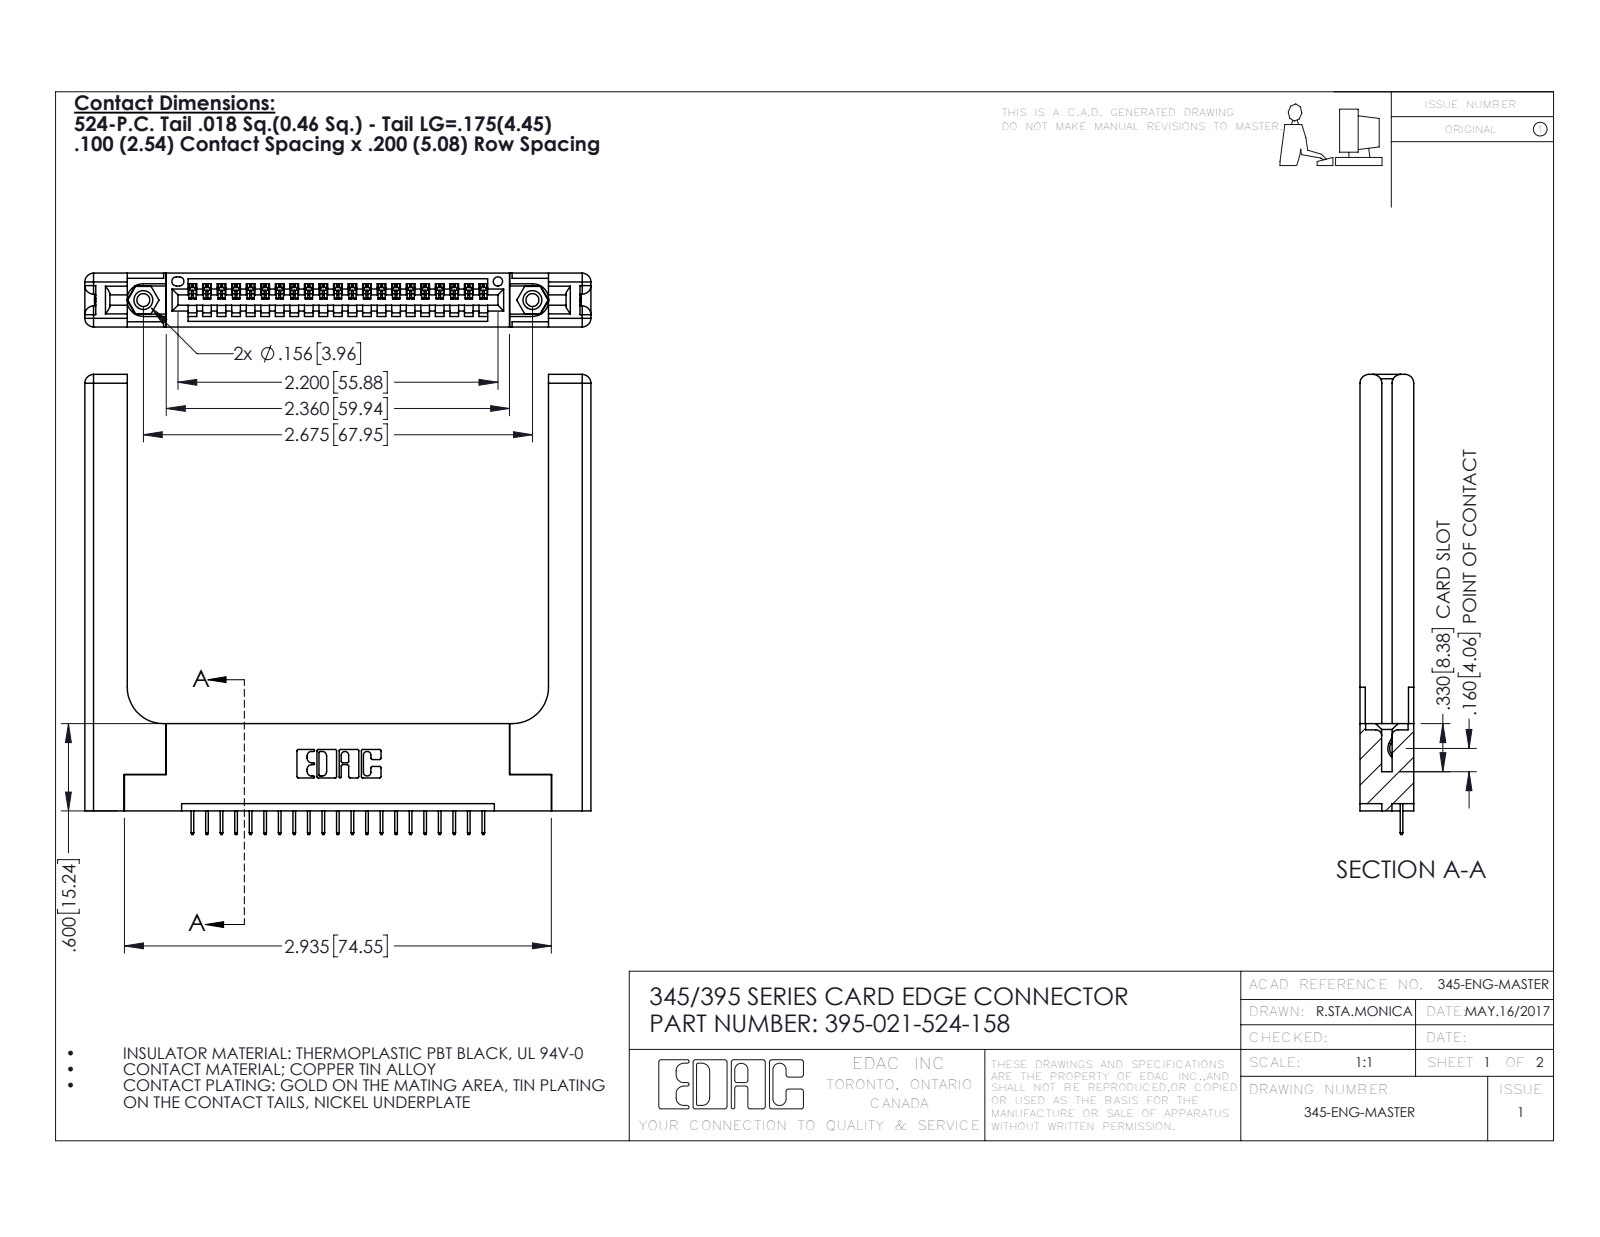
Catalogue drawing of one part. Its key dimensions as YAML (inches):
part_name: "345-220-058_345-220-058; 345-292-001_345-293-124; 395-021-524-158; 345 Part_Flush Mounting Lugs - 0.156 Dia-TH (+1 more)"
step_written_by: "SolidWorks 2016 (CONFIG_CONTROL_DESIGN)"
units: inches
bodies: {solids: 26, faces: 1684, planar: 1194, cylindrical: 430, other: 60}
overall_size: [3.479, 3.162, 0.37]
volume: 1.016
surface_area: 24.13
round_holes:
  - {diameter: 0.089, count: 2}
  - {diameter: 0.125, count: 2}
  - {diameter: 0.156, count: 2}
  - {diameter: 0.064, count: 1}
round_bosses_or_shafts:
  - {diameter: 0.155, count: 2}
partial_cylinders:
  - {radius: 0.006, count: 42}
  - {radius: 0.01, count: 22}
  - {radius: 0.06, count: 16}
  - {radius: 0.007, count: 6}
  - {radius: 0.031, count: 6}
  - {radius: 0.026, count: 3}
  - {radius: 0.03, count: 2}
  - {radius: 0.031, count: 2}
face_to_face_distances: [0.37, 0.072, 0.298, 0.148, 0.15, 0.2, 0.077, 0.22, 0.098, 0.272]
hole_center_spacings: [0.27, 2.441, 2.675]
